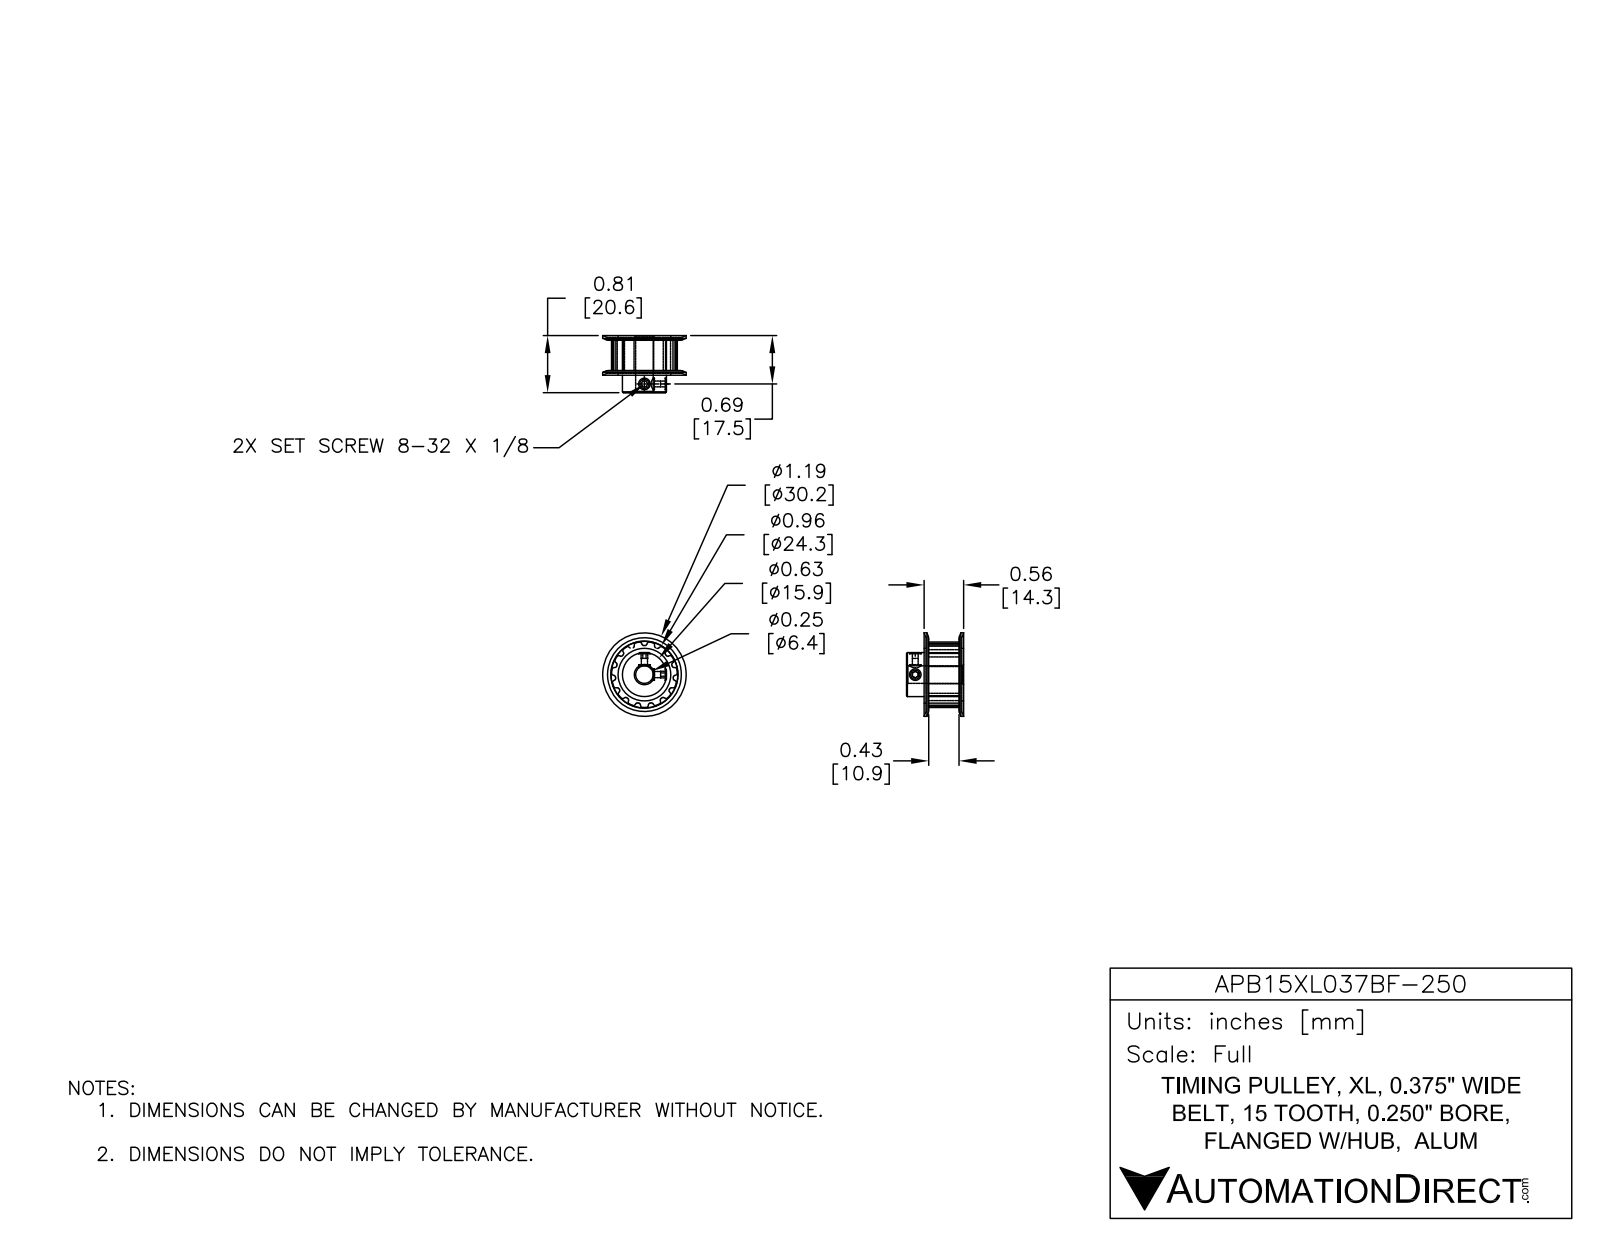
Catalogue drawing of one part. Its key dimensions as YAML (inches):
part_name: "APB15XL037BF-250"
step_written_by: "SolidWorks 2014 (AUTOMOTIVE_DESIGN)"
units: inches
bodies: {solids: 1, faces: 171, planar: 51, cylindrical: 98, other: 22}
overall_size: [1.188, 1.188, 0.813]
volume: 0.396
surface_area: 6.267
round_holes:
  - {diameter: 0.088, count: 2}
  - {diameter: 0.25, count: 1}
round_bosses_or_shafts:
  - {diameter: 0.625, count: 1}
partial_cylinders:
  - {radius: 0.015, count: 60}
  - {radius: 0.413, count: 1}
face_to_face_distances: [0.495, 0.033, 0.528, 0.813, 0.78, 0.285, 0.462, 0.318, 0.065, 0.032]
